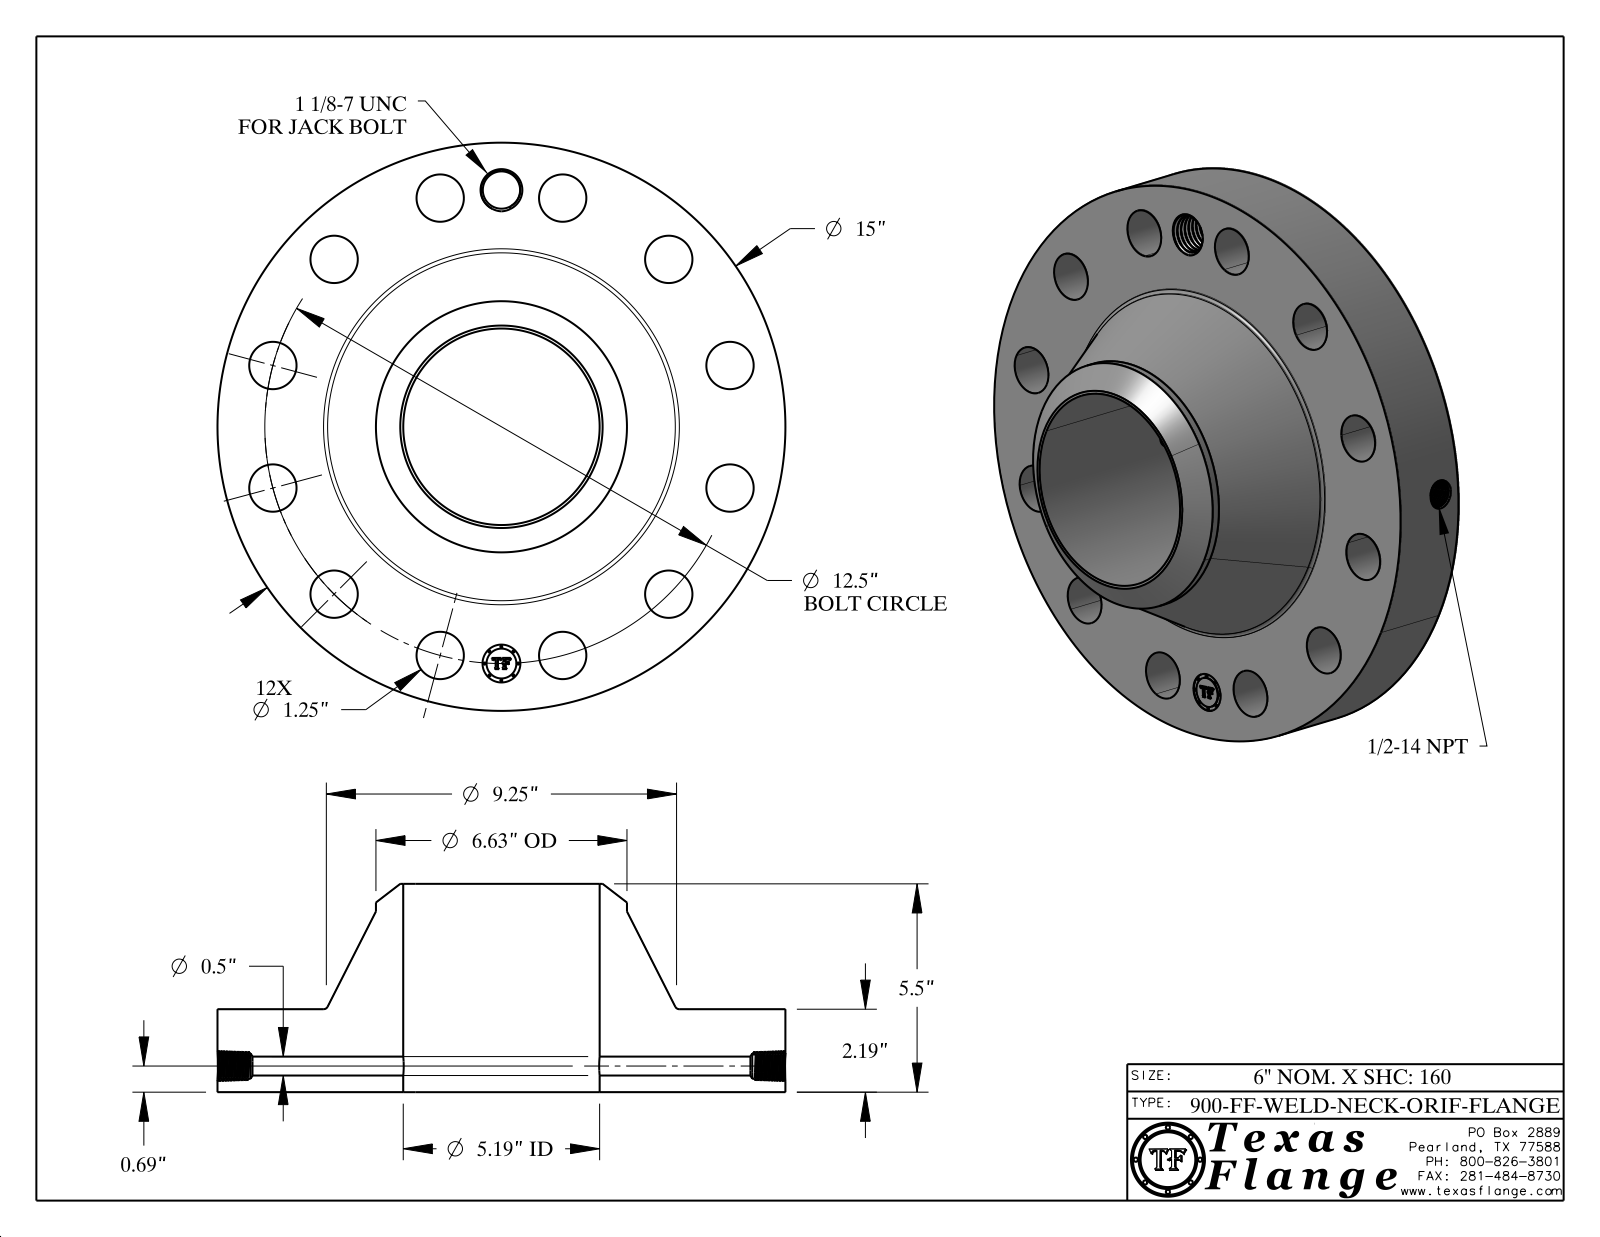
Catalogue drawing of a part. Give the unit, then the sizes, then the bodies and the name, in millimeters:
Units: millimetres
Overall size (bounding box): 381 × 381 × 139.7
Round holes (diameter × count): ⌀31.8 ×12, ⌀12.7 ×1, ⌀17.1 ×1, ⌀25 ×1, ⌀25.4 ×1, ⌀131.7 ×1
Round bosses / shafts (diameter × count): ⌀1.5 ×8, ⌀381 ×1, ⌀168.4 ×1, ⌀20 ×1
Main face-to-face distances: 55.6, 139.7, 84.1, 55.2, 0.4, 84.5, 7.6, 7.4, 1.4, 6.3
Hole centre spacings: 158.8, 306.7, 82.2, 224.5, 275, 317.5, 41.4, 82.2
Volume: 6 314 000 mm³ · Surface area: 420 800 mm²
Bodies: 1 solid, 777 faces (368 planar, 100 cylindrical, 309 other)
Part name (STEP PRODUCT): 900-FF-WELD-NECK
STEP written by: CATIA V5 STEP AP214 (AUTOMOTIVE_DESIGN)
